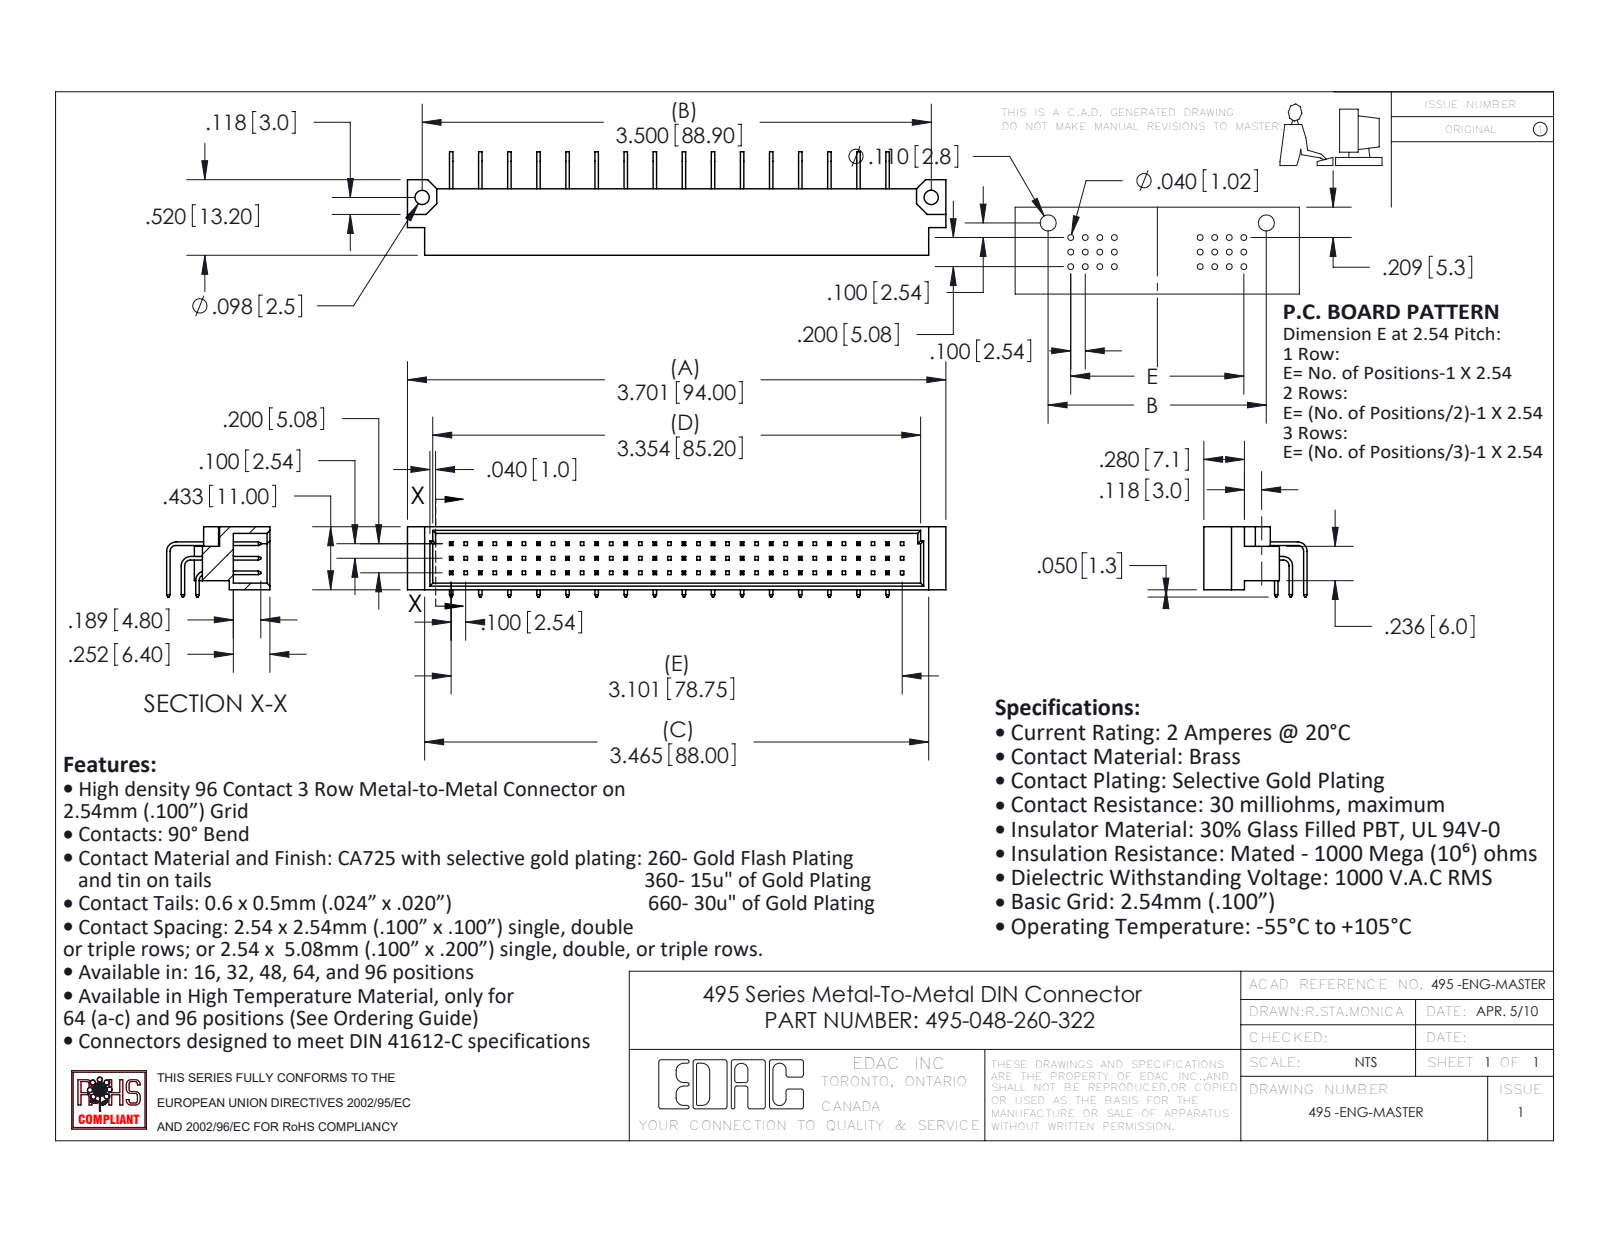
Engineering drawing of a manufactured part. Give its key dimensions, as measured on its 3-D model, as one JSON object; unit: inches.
{"part_name": "495 Part_96; 495-290-3; 495-290-2; 495-290-1 (+1 more)", "step_written_by": "SolidWorks 2020 (AUTOMOTIVE_DESIGN)", "units": "inches", "bodies": {"solids": 49, "faces": 1297, "planar": 1197, "cylindrical": 100, "other": 0}, "overall_size": [3.701, 0.711, 0.483], "volume_in3": 0.383, "surface_area_in2": 14.17, "round_holes": [[0.098, 2]], "partial_cylinders_radius": [[0.04, 3], [0.065, 3]], "face_to_face_distances": [0.2, 0.045, 0.388, 0.1, 0.205, 0.024, 0.433, 0.4, 0.6, 0.8], "hole_center_spacings": [3.5]}
